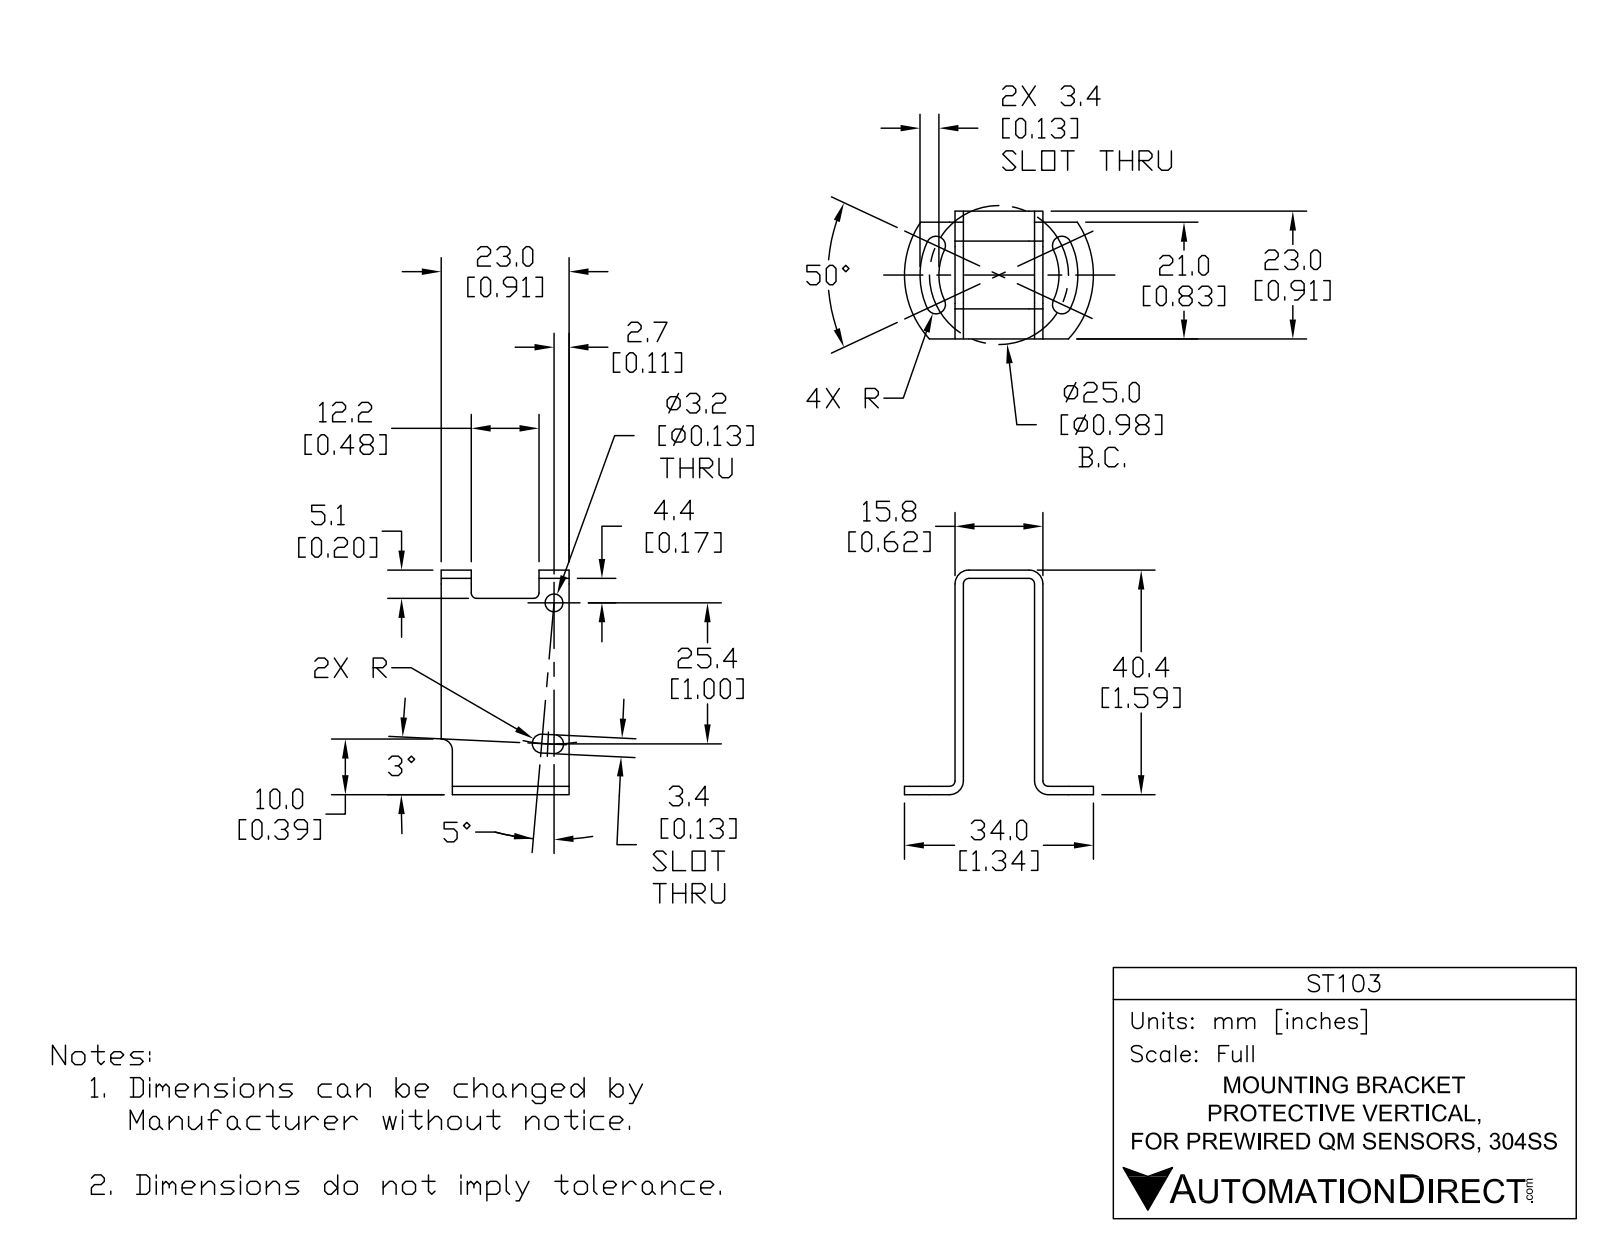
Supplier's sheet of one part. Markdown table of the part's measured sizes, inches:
| quantity | value |
| --- | --- |
| part name | ST103 |
| STEP written by | SolidWorks 2017 (AUTOMOTIVE_DESIGN) |
| units | inches |
| bodies | 1 solid, 61 faces (20 planar, 41 cylindrical, 0 other) |
| overall size | 1.591 × 1.339 × 0.906 |
| volume | 0.182 in³ |
| surface area | 7.19 in² |
| round holes (diameter × count) | 0.126 × 1 |
| partial cylindrical surfaces (radius × count) | 0.079 × 5, 0.02 × 4, 0.067 × 4, 0.063 × 2, 0.425 × 1, 0.559 × 1, 0.669 × 1, 0.937 × 1 |
| main face-to-face distances | 0.059, 0.563, 0.622, 0.504, 1.531, 1.591, 1.472, 0.906, 0.213, 0.693 |
